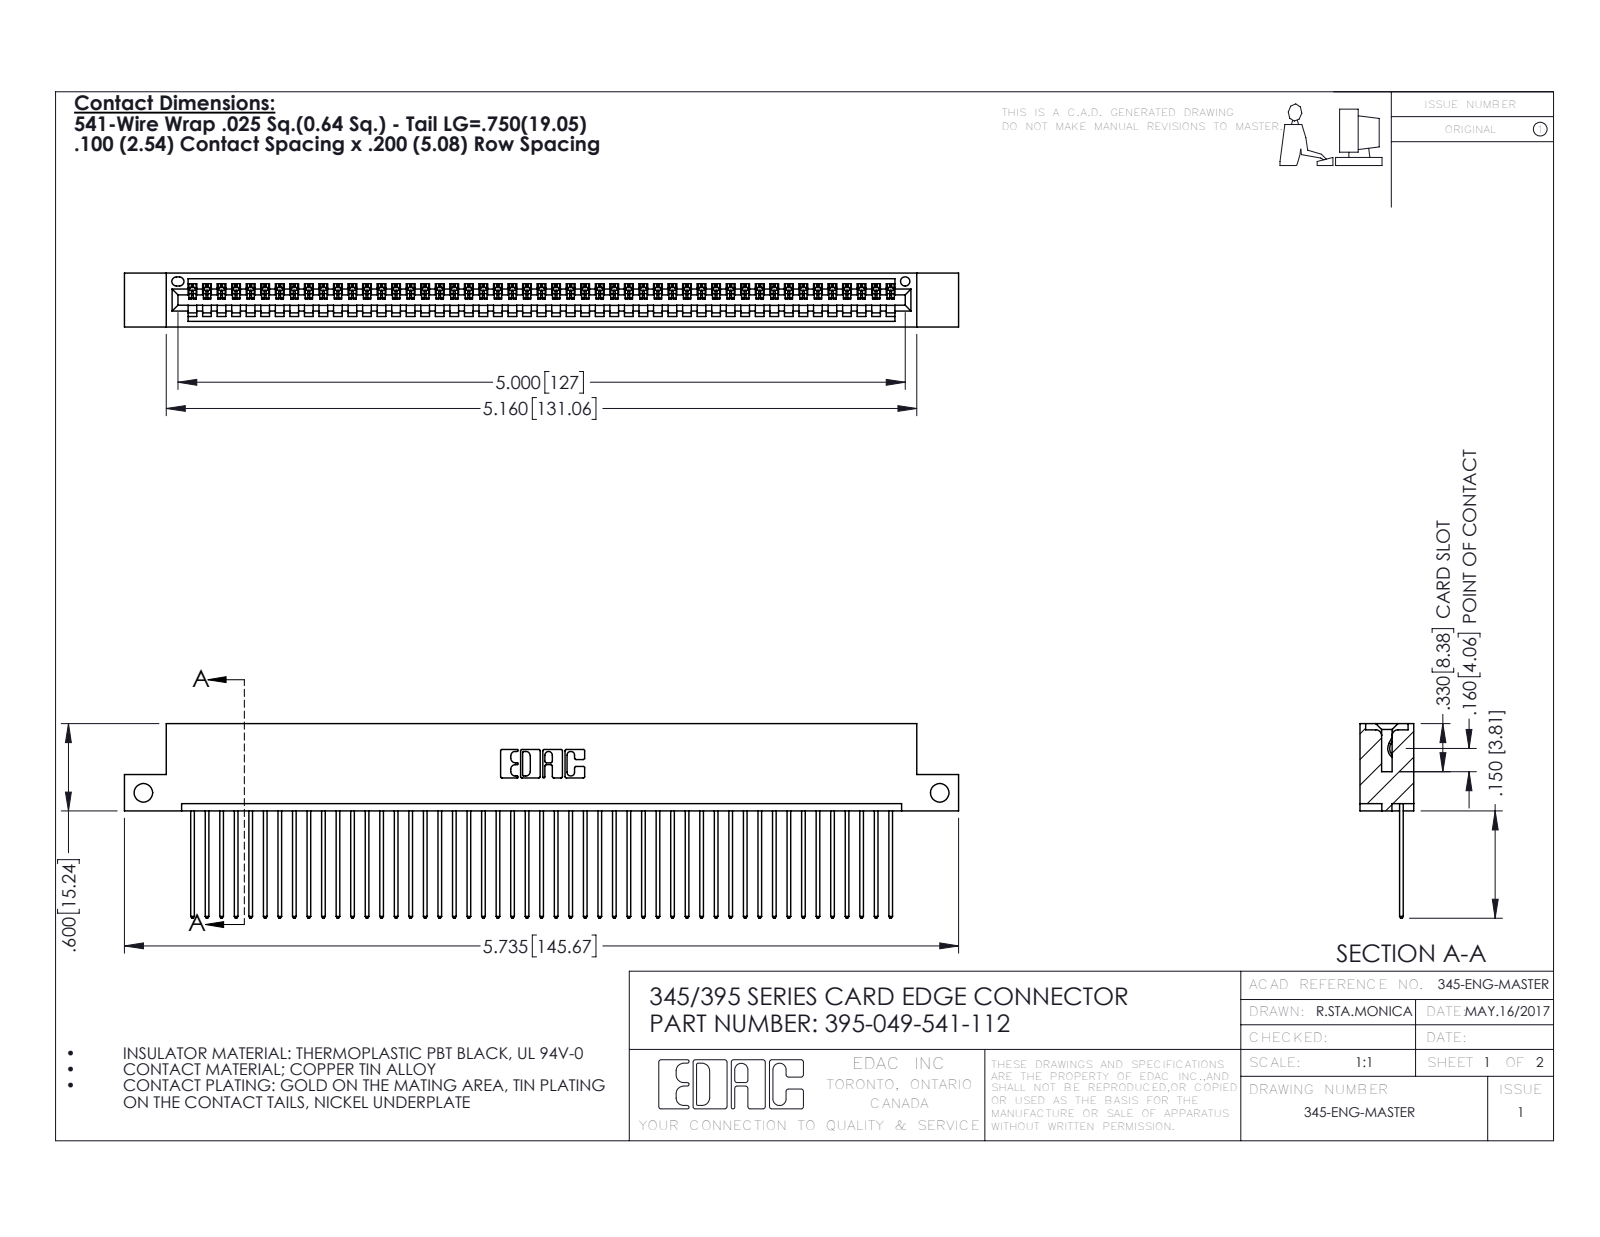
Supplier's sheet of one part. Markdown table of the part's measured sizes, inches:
| quantity | value |
| --- | --- |
| part name | 345-292-001_345-293-141; 345 Part_Flush Mounting Lugs - Side Mount; 395-049-541-112 |
| STEP written by | SolidWorks 2016 (CONFIG_CONTROL_DESIGN) |
| units | inches |
| bodies | 50 solids, 2968 faces (2040 planar, 928 cylindrical, 0 other) |
| overall size | 5.735 × 1.337 × 0.37 |
| volume | 0.852 in³ |
| surface area | 30.17 in² |
| round holes (diameter × count) | 0.128 × 2, 0.064 × 1 |
| partial cylindrical surfaces (radius × count) | 0.006 × 98, 0.01 × 98, 0.01 × 22, 0.007 × 6, 0.031 × 6, 0.026 × 3, 0.031 × 2, 0.04 × 2 |
| main face-to-face distances | 0.072, 0.298, 0.098, 0.272, 0.025, 0.2, 0.37, 0.225, 0.149, 0.072 |
| hole center spacings | 5.475 |
